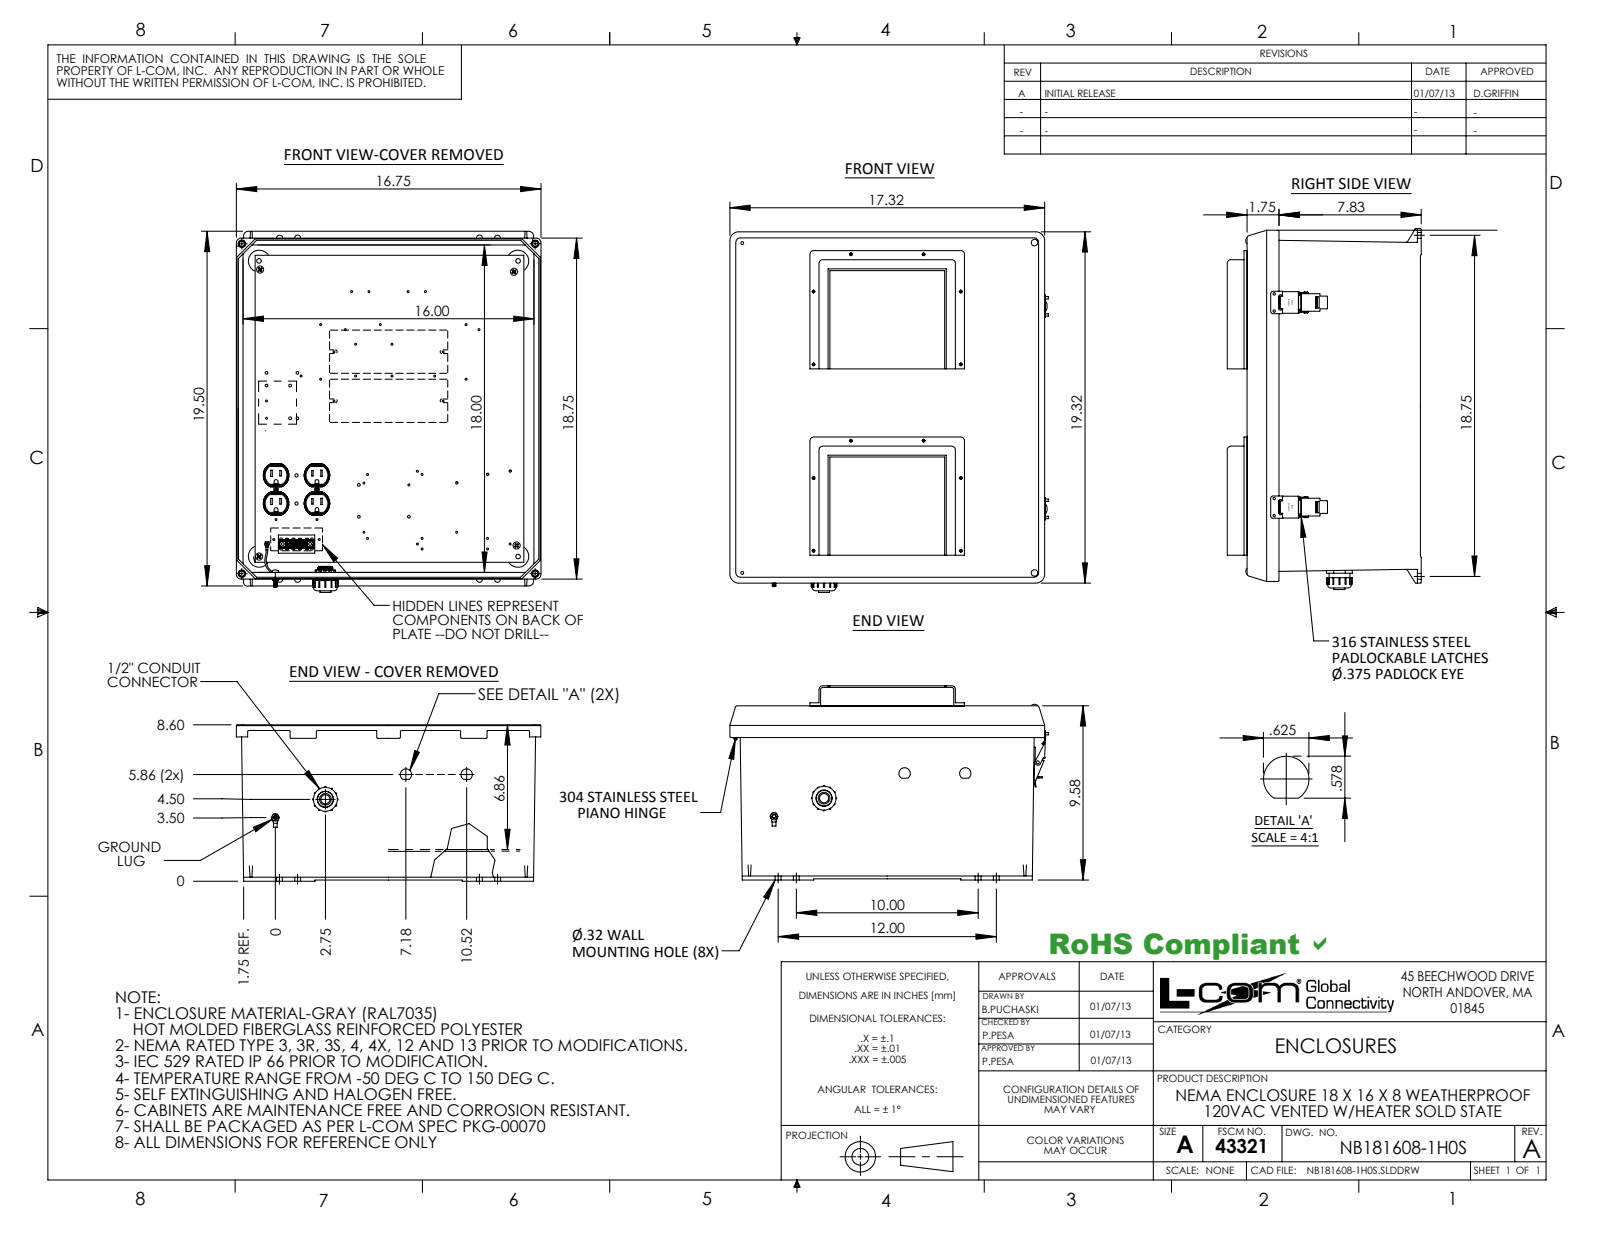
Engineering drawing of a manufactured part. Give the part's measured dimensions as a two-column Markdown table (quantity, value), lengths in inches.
| quantity | value |
| --- | --- |
| part name | NB181608-1H0S; HYP295; XFN-0021; XFW-0004 (+8 more) |
| STEP written by | SolidWorks 2012 (AUTOMOTIVE_DESIGN) |
| units | inches |
| bodies | 67 solids, 6534 faces (2173 planar, 1729 cylindrical, 2632 other) |
| overall size | 27.69 × 22.487 × 19.797 |
| volume | 252.5 in³ |
| surface area | 3 516 in² |
| round holes (diameter × count) | 0.107 × 42, 0.15 × 12, 0.18 × 8, 0.315 × 8, 0.07 × 6, 0.018 × 4, 0.05 × 4, 0.125 × 4, 0.13 × 4, 0.164 × 4, 0.164 × 4, 0.2 × 4 |
| round bosses / shafts (diameter × count) | 0.262 × 13, 0.44 × 4, 0.42 × 4, 0.382 × 4, 0.366 × 4, 0.351 × 4, 0.347 × 4, 0.26 × 4 |
| partial cylindrical surfaces (radius × count) | 0.03 × 144, 0.02 × 56, 0.015 × 47, 0.01 × 42, 0.315 × 40, 0.039 × 38, 0.048 × 32, 0.005 × 16 |
| main face-to-face distances | 0.118, 1.618, 1.5, 0.1, 1.718, 1.6, 0.126, 0.402, 0.039, 0.276 |
| hole center spacings | 1.004, 1.317, 1.675, 2.079, 2.463, 3.075, 11.004, 12.19 |
